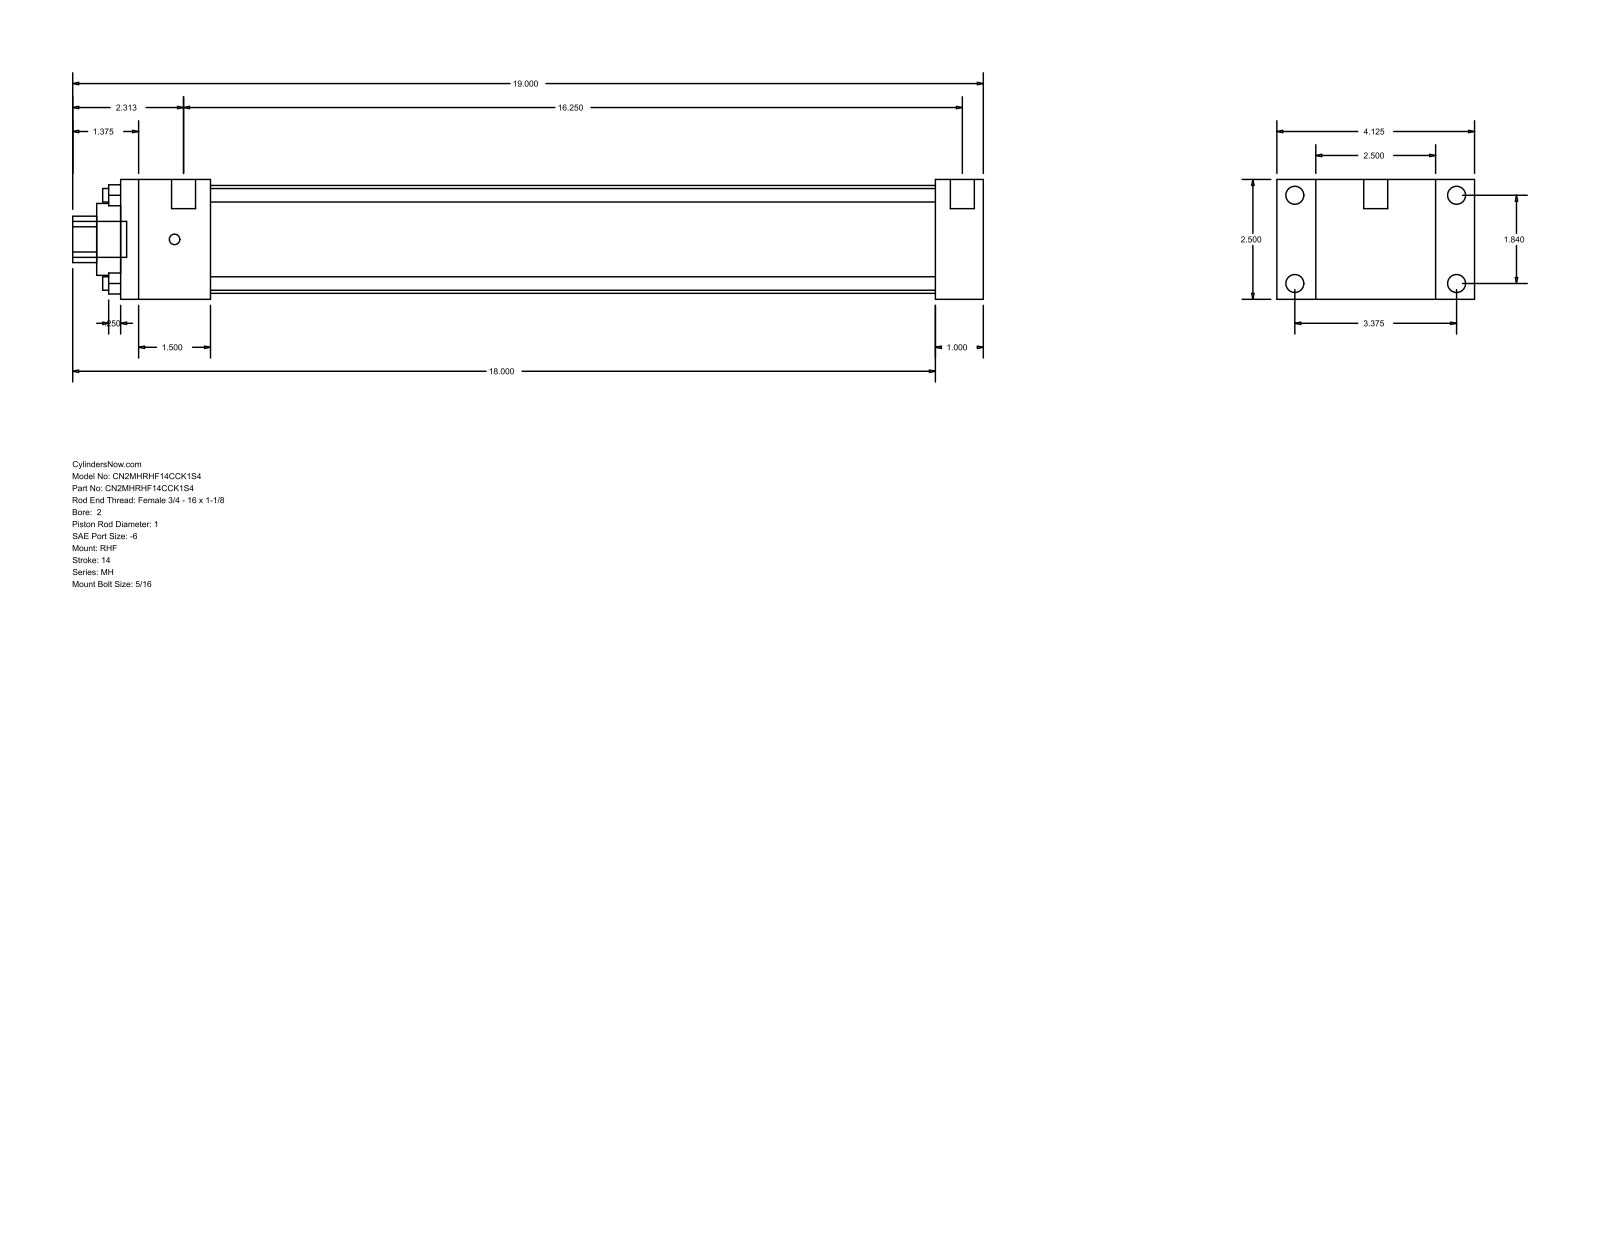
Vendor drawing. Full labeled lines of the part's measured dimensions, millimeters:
Part name (STEP PRODUCT): MH_RHF__0200_1
STEP written by: GSSL Pune (CONFIG_CONTROL_DESIGN)
Units: millimetres
Bodies: 0 solids, 88 faces (60 planar, 28 cylindrical, 0 other)
Overall size (bounding box): 482.6 × 104.78 × 63.5
Round holes (diameter × count): ⌀7.14 ×4, ⌀25.4 ×1, ⌀38.1 ×1, ⌀57.15 ×1
Round bosses / shafts (diameter × count): ⌀9.53 ×4, ⌀5.56 ×4, ⌀12.7 ×2, ⌀19.05 ×1
Partial cylindrical surfaces — rounded edges, fillets, slot ends (radius × count): R12.29 ×1
Main face-to-face distances: 63.5, 25.4, 20.64, 84.14, 457.2, 431.8, 104.78, 47.63, 384.17, 409.57
Hole centre spacings: 33.05, 46.74, 66.1
